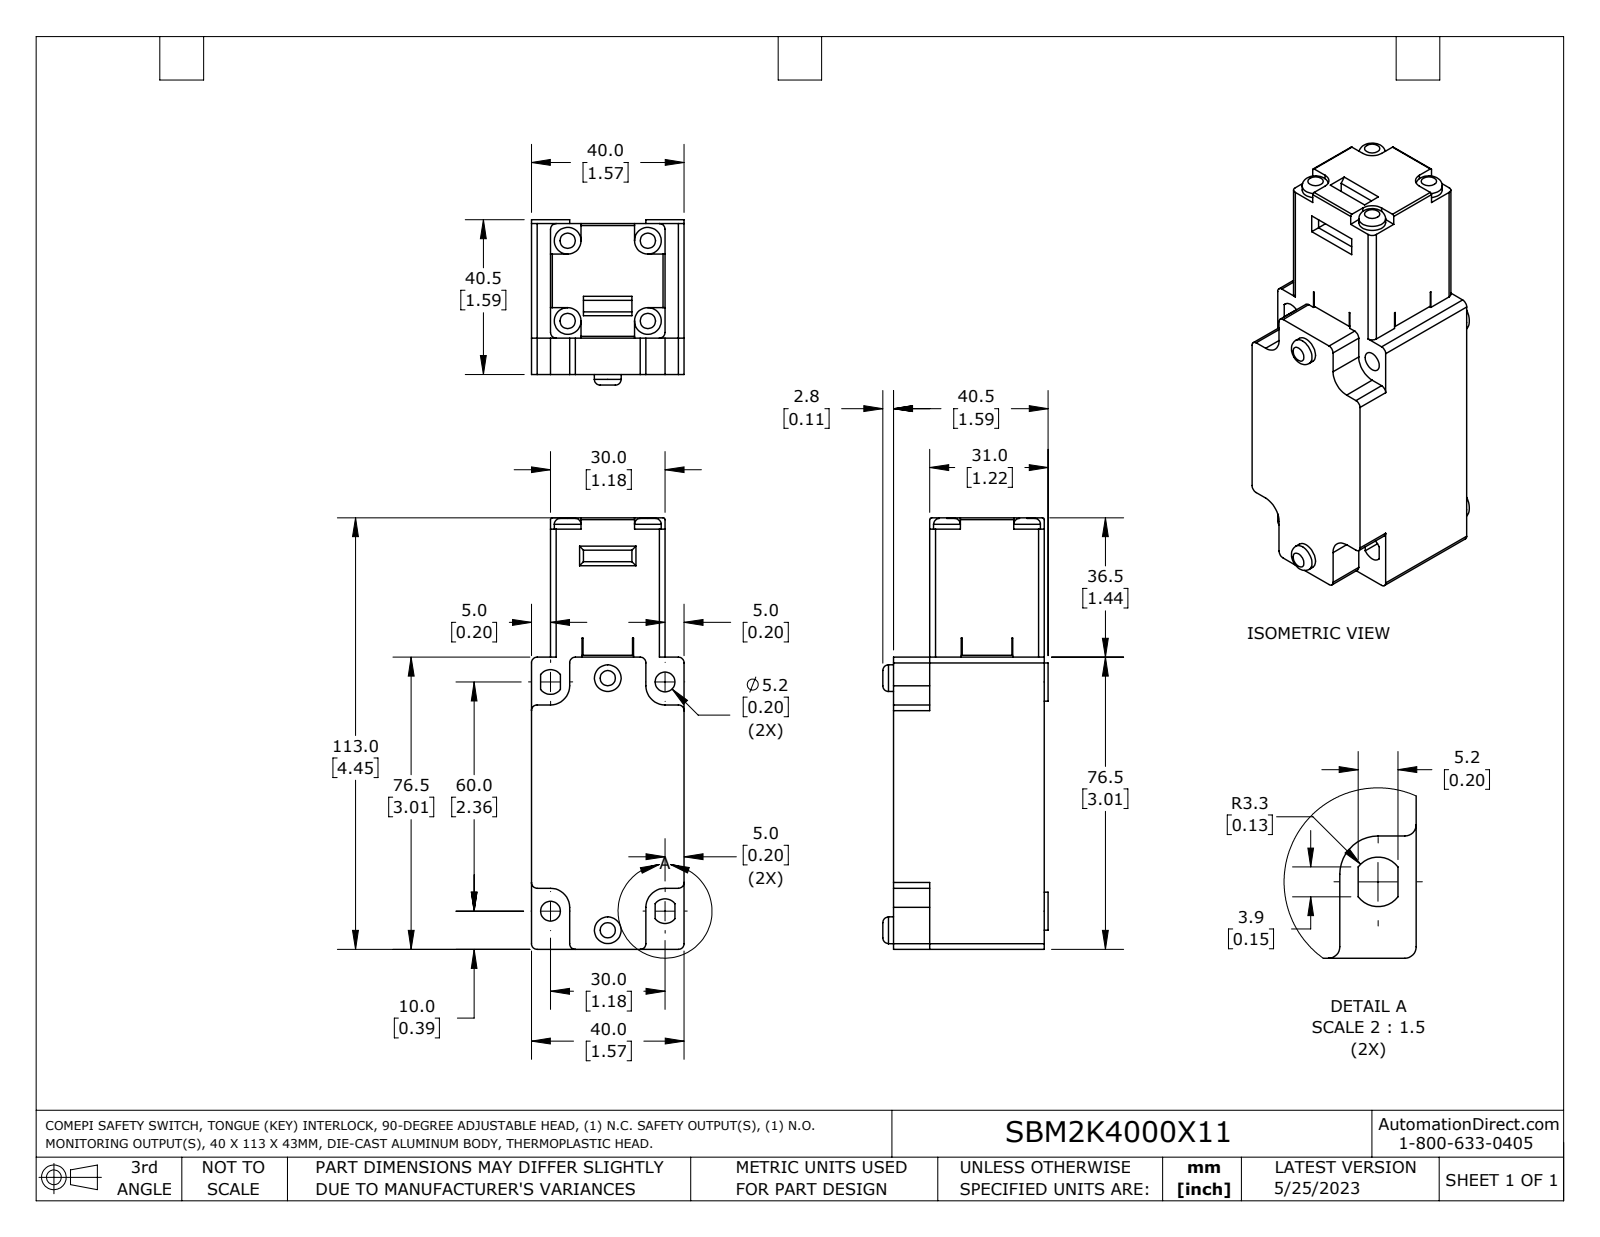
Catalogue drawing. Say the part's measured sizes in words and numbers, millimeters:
The part is named "SBM2K4000X11". Its 3-D file was written by "SolidWorks 2021 (AUTOMOTIVE_DESIGN)". It is 1 solid with 147 faces: 86 planar, 54 cylindrical and 7 other. Overall it measures 113 by 43.3 by 40 millimeters. Its volume is 139 400 cubic millimeters and its surface area 25 930 square millimeters. Round holes: 4 of diameter 7, 2 of diameter 5.2, 1 of diameter 17, 1 of diameter 19. Round bosses or shafts: 4 of diameter 10, 2 of diameter 7. Partial cylindrical surfaces (rounded edges, fillets, slot ends): 16 of radius 1.5, 4 of radius 0.5, 4 of radius 5, 2 of radius 3.3, 1 of radius 11.5, 1 of radius 12. The main face-to-face distances are 30, 40, 39.5, 5, 35, 9.5, 76.5, 3, 0.5, 25. The hole center spacings are 21, 14.1, 15.6, 29.7, 67.1.
